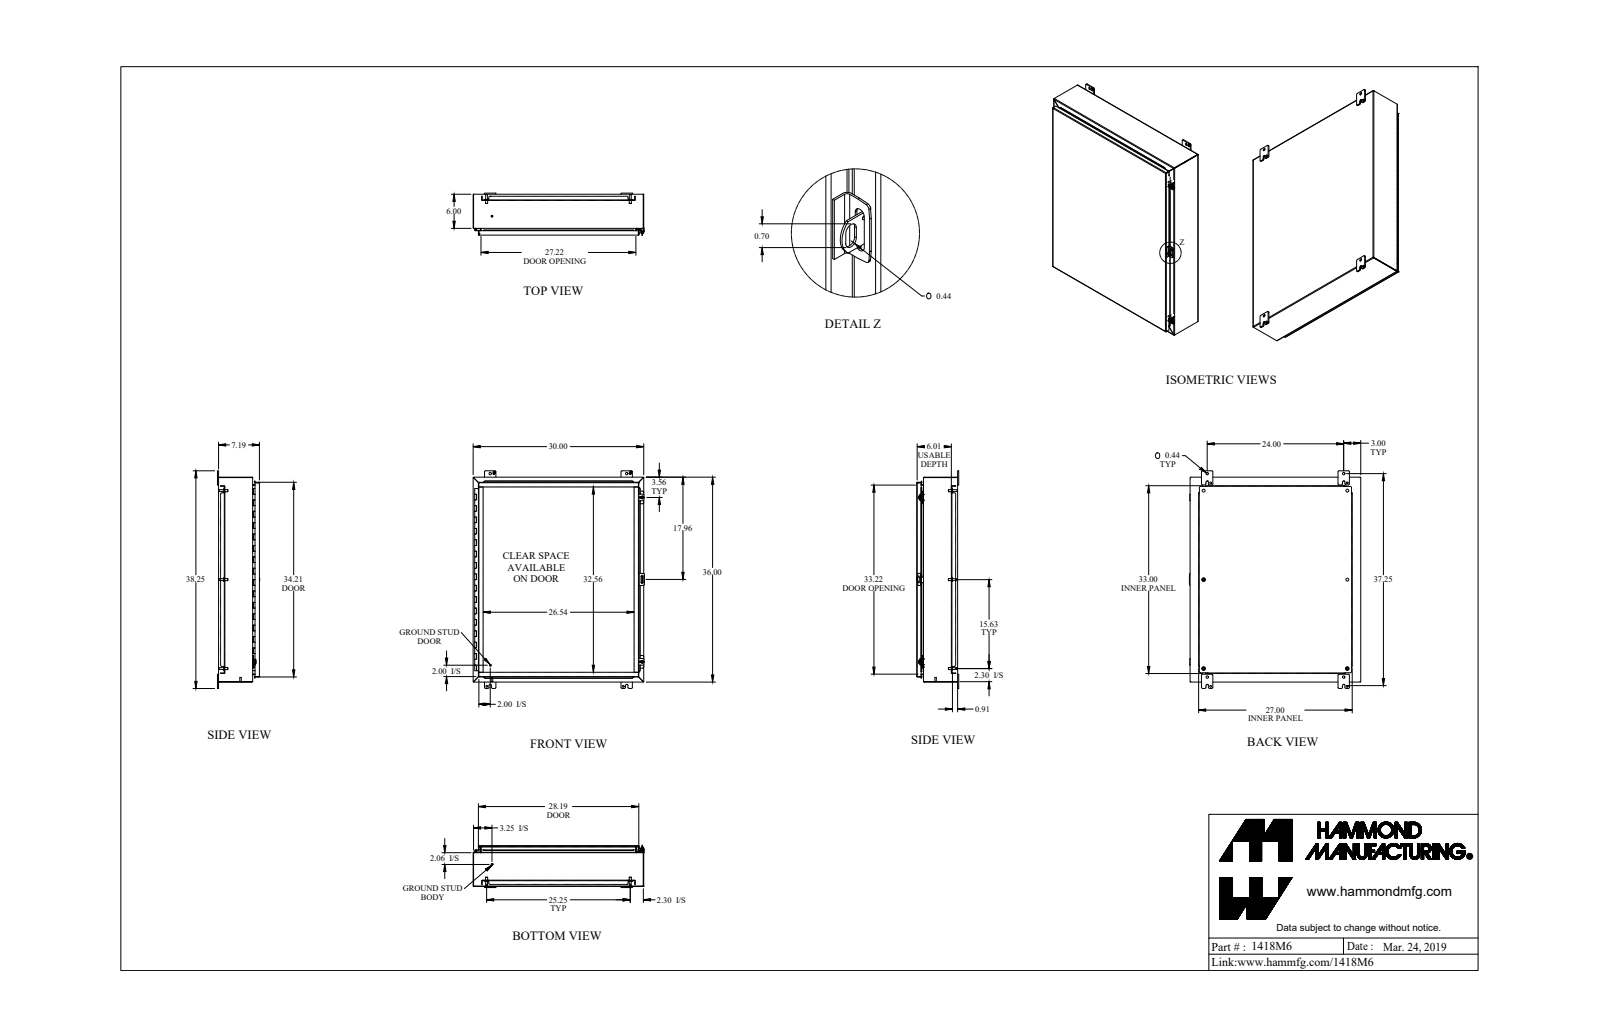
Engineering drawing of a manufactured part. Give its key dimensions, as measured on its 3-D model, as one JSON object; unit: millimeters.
{"part_name": "1418M6_Default", "step_written_by": "SolidWorks 2019 (CONFIG_CONTROL_DESIGN)", "units": "millimeters", "bodies": {"solids": 47, "faces": 1436, "planar": 853, "cylindrical": 499, "other": 84}, "overall_size": [971.6, 765.2, 188.9], "volume_mm3": 6037000, "surface_area_mm2": 6125000, "round_holes": [[12.7, 6], [7.8, 4], [8, 4], [11.1, 4], [11.3, 4], [5.4, 2], [6.7, 2], [9.5, 2], [3.2, 1], [4.7, 1]], "round_bosses_or_shafts": [[16.5, 6], [9.5, 6], [8.4, 6], [25.4, 4], [12.7, 2], [9.9, 2], [7.1, 2], [6.4, 2]], "partial_cylinders_radius": [[4.8, 38], [0.9, 24], [2.7, 24], [6.4, 16], [1.2, 13], [3.6, 13], [2.9, 12], [1.1, 8]], "face_to_face_distances": [1.8, 180.7, 178.8, 182.5, 2.4, 23.8, 25.6, 154.5, 152.6, 26.2], "hole_center_spacings": [641.4, 396.9, 609.6, 754.2, 1093.7, 696, 793.8, 793.8]}
